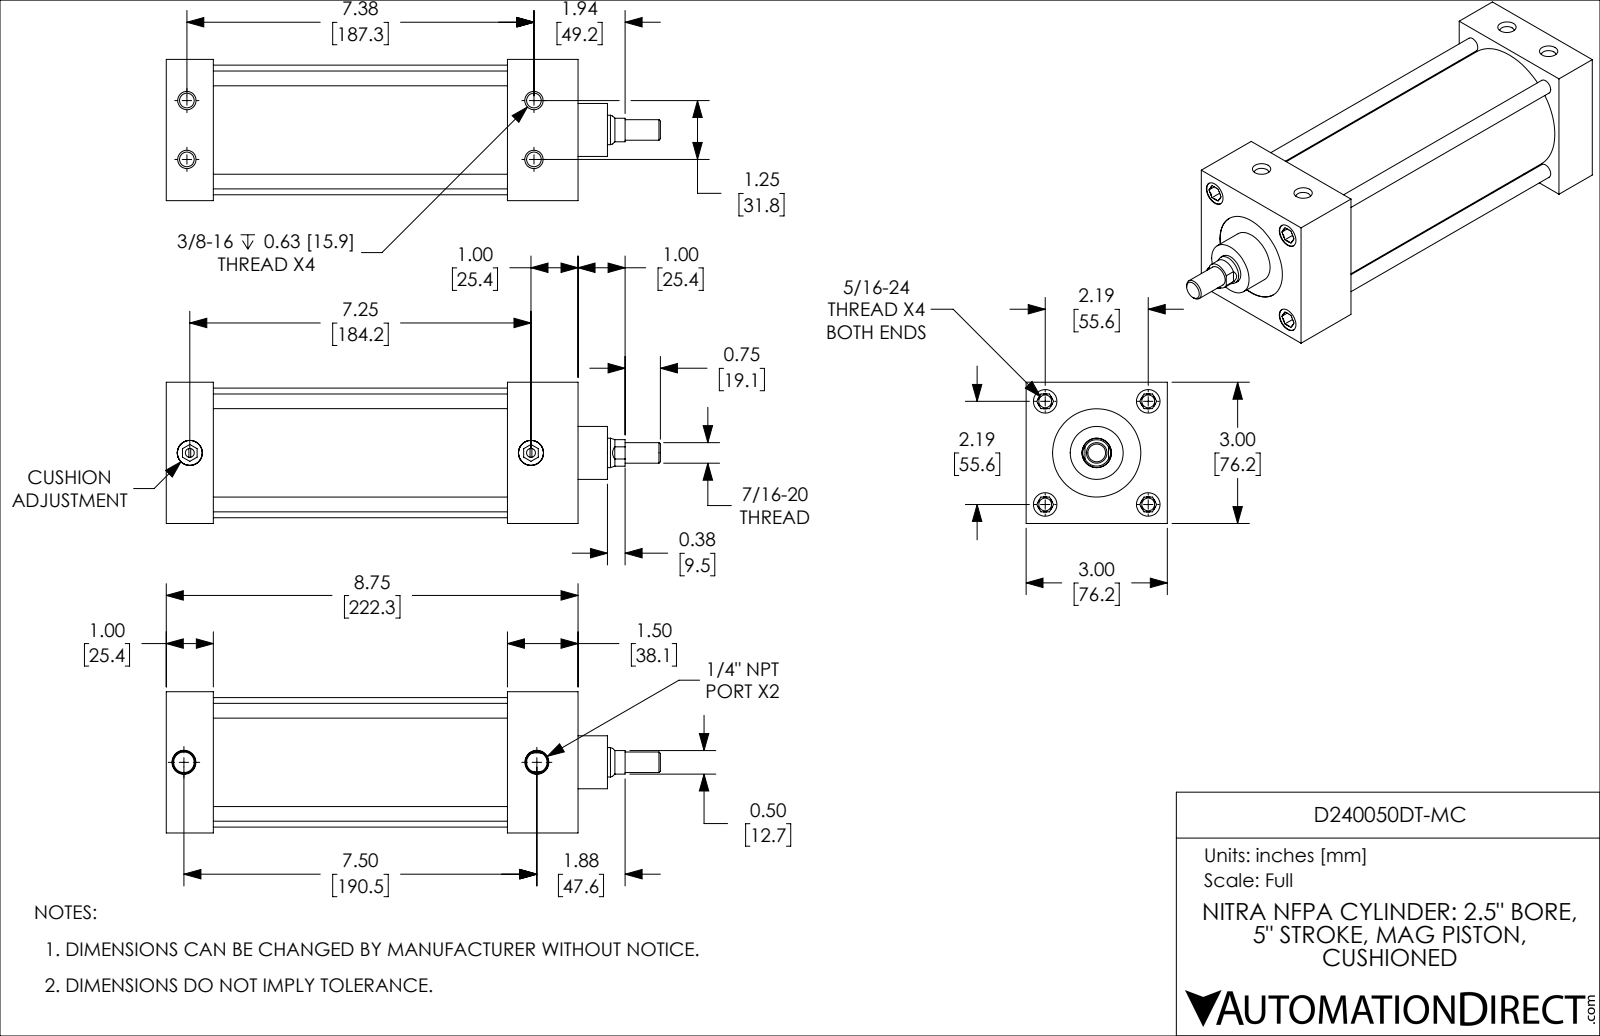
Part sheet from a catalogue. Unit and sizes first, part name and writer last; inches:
Units: inches
Overall size (bounding box): 10.5 × 3 × 3
Round holes (diameter × count): ⌀0.272 ×4, ⌀0.313 ×4, ⌀0.5 ×4, ⌀0.19 ×2, ⌀0.438 ×2, ⌀0.531 ×2, ⌀0.626 ×1, ⌀1.875 ×1, ⌀2.501 ×1
Round bosses / shafts (diameter × count): ⌀0.312 ×4, ⌀0.532 ×2, ⌀2.751 ×1, ⌀2.499 ×1, ⌀1.125 ×1, ⌀0.624 ×1, ⌀0.437 ×1
Partial cylindrical surfaces — rounded edges, fillets, slot ends (radius × count): R0.281 ×1
Main face-to-face distances: 3, 1, 7.25, 6.25, 8.75, 7.75, 1.5, 1.25, 2.25, 5
Hole centre spacings: 1.548, 2.19, 0.628, 0.628, 1.25, 3.097, 7.375, 7.464
Volume: 38.22 in³ · Surface area: 246.1 in²
Bodies: 4 solids, 248 faces (90 planar, 78 cylindrical, 80 other)
Part name (STEP PRODUCT): D240050DT-MC_PISTON_KK1; D240050DT-MC; D240050DT-MC_CUSHION; D240050DT-MC_BODY
STEP written by: SolidWorks 2019 (CONFIG_CONTROL_DESIGN)
